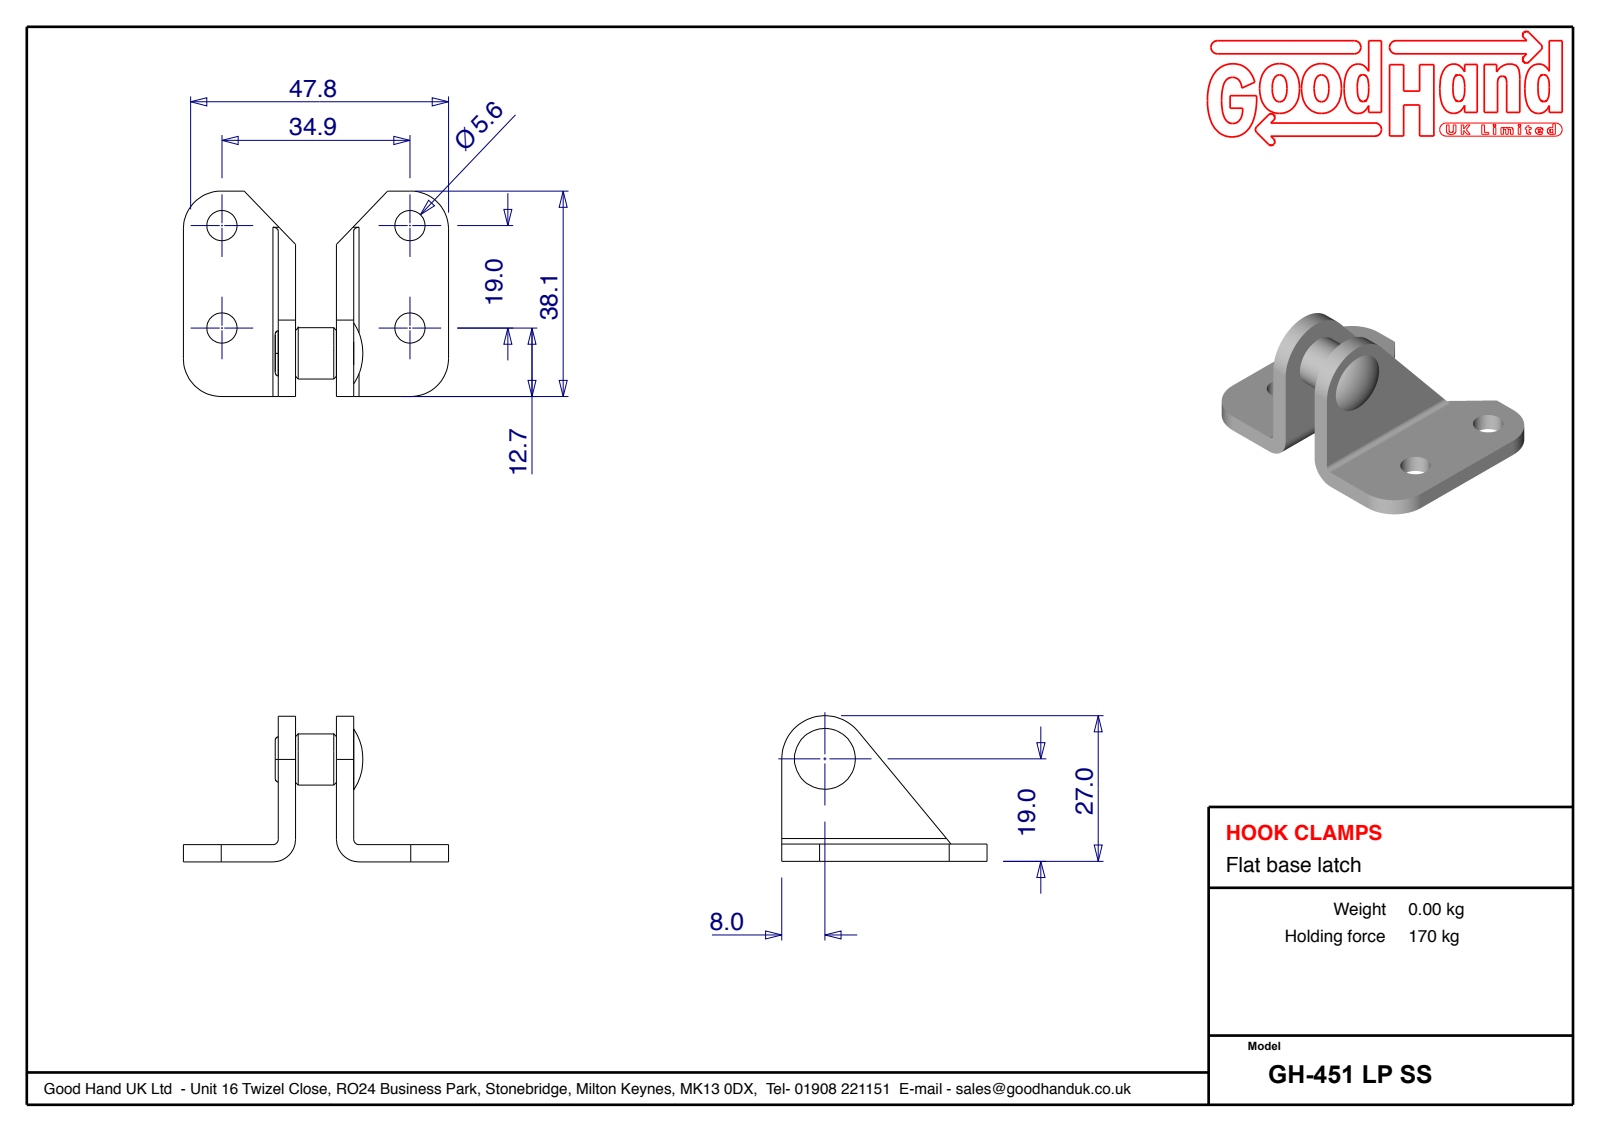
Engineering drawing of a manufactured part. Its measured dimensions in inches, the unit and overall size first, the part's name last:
Units: inches
Overall size (bounding box): 1.937 × 1.5 × 1.063
Round holes (diameter × count): ⌀0.22 ×4, ⌀0.252 ×1, ⌀0.256 ×1
Round bosses / shafts (diameter × count): ⌀0.374 ×1
Partial cylindrical surfaces — rounded edges, fillets, slot ends (radius × count): R0.276 ×4, R0.039 ×2, R0.165 ×2, R0.315 ×1
Main face-to-face distances: 0.126, 0.425, 0.299, 0.551, 0.693, 0.819, 1.118, 1.244, 1.937, 1.5
Hole centre spacings: 0.748, 1.374, 1.565
Volume: 0.449 in³ · Surface area: 9.424 in²
Bodies: 3 solids, 54 faces (20 planar, 26 cylindrical, 8 other)
STEP written by: Spatial InterOp 3D (automotive_design)
